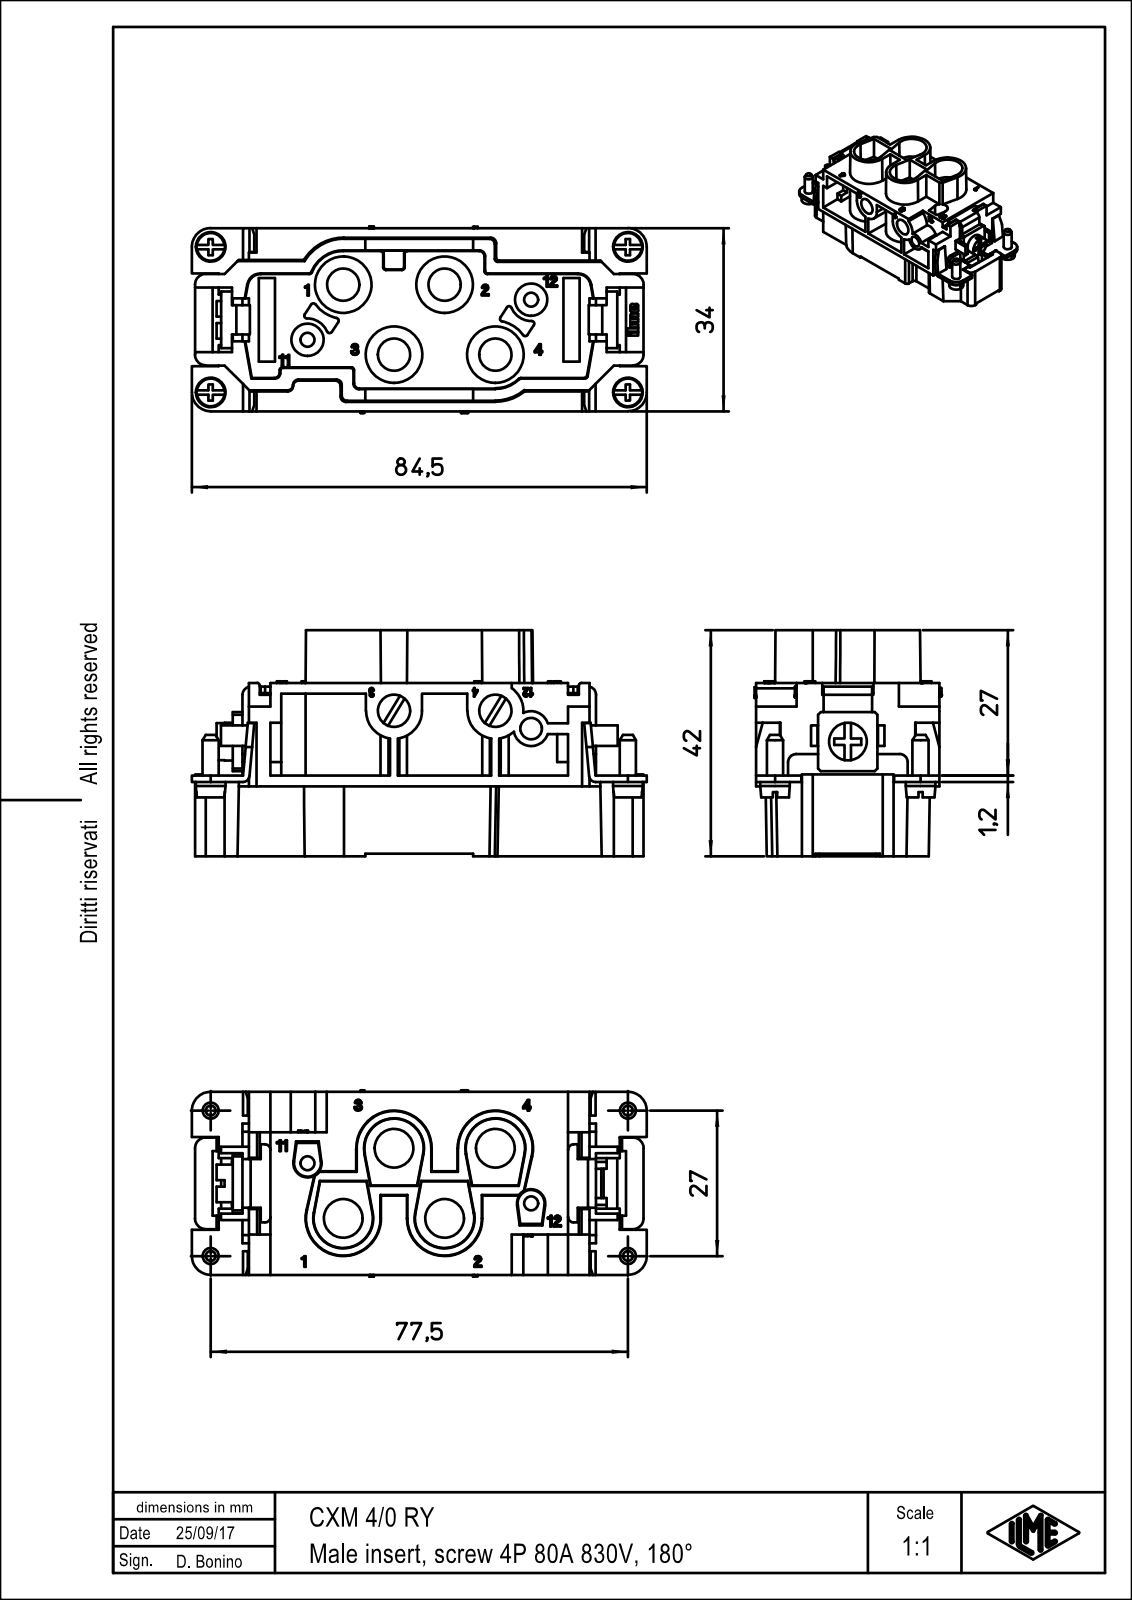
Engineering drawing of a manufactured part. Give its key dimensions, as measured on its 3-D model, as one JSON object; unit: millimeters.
{"part_name": "CXM_4-0_RY", "step_written_by": "PTC Creo Elements/Direct Modeling 19.0B 21-Mar-2015 (C) Parametric Technology GmbH (AUTOMOTIVE_DESIGN)", "units": "millimeters", "bodies": {"solids": 1, "faces": 1430, "planar": 1228, "cylindrical": 162, "other": 40}, "overall_size": [84.4, 42, 34.6], "volume_mm3": 40786, "surface_area_mm2": 28600, "round_holes": [[6, 6], [7.2, 4], [10.5, 4], [4, 3], [2.6, 2]], "round_bosses_or_shafts": [[6, 4], [5.5, 4], [3, 4], [7, 1]], "partial_cylinders_radius": [[0.5, 21], [1, 12], [2, 6], [0.29, 5], [1.5, 4], [2.5, 4], [3.5, 4], [5.2, 4]], "face_to_face_distances": [2, 17.2, 2.6, 1.2, 15, 19.8, 21, 34, 14, 13], "hole_center_spacings": [18.8, 9.4, 16.04, 7.42, 16.29, 16.39, 25.66, 27.43]}
